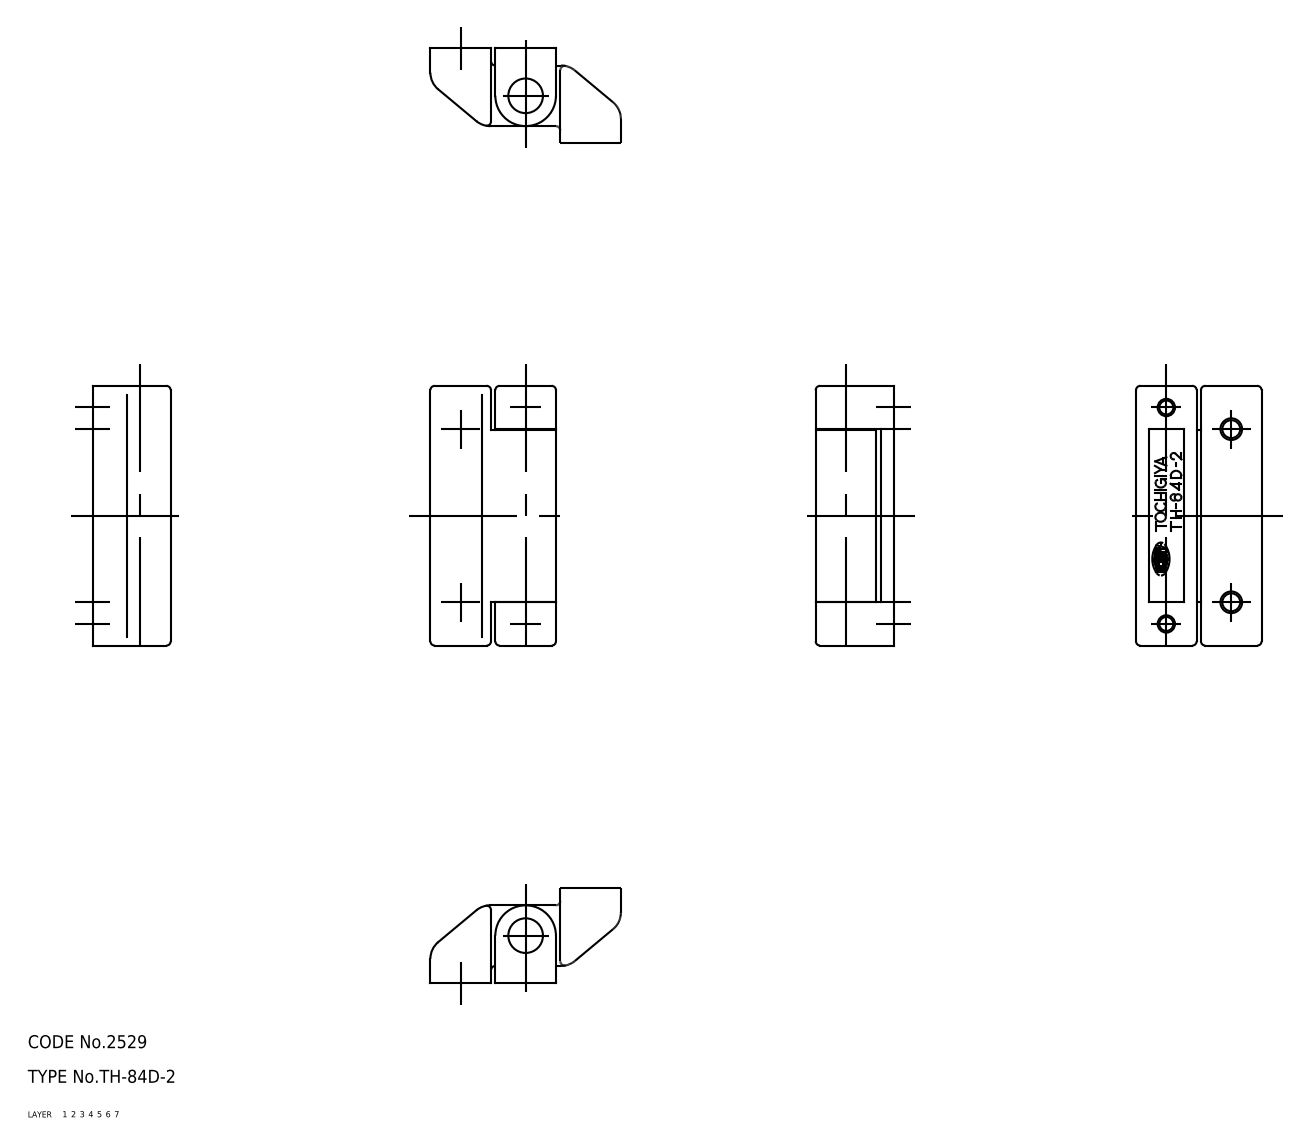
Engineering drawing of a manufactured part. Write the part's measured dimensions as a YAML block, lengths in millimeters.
part_name: "shaft; hinge piece_B; hinge piece_A; TH_84D_2_18088_36"
step_written_by: "CADfix (AUTOMOTIVE_DESIGN)"
units: millimeters
bodies: {solids: 3, faces: 78, planar: 0, cylindrical: 0, other: 78}
overall_size: [60, 29.01, 18]
volume: 24731
surface_area: 11593
